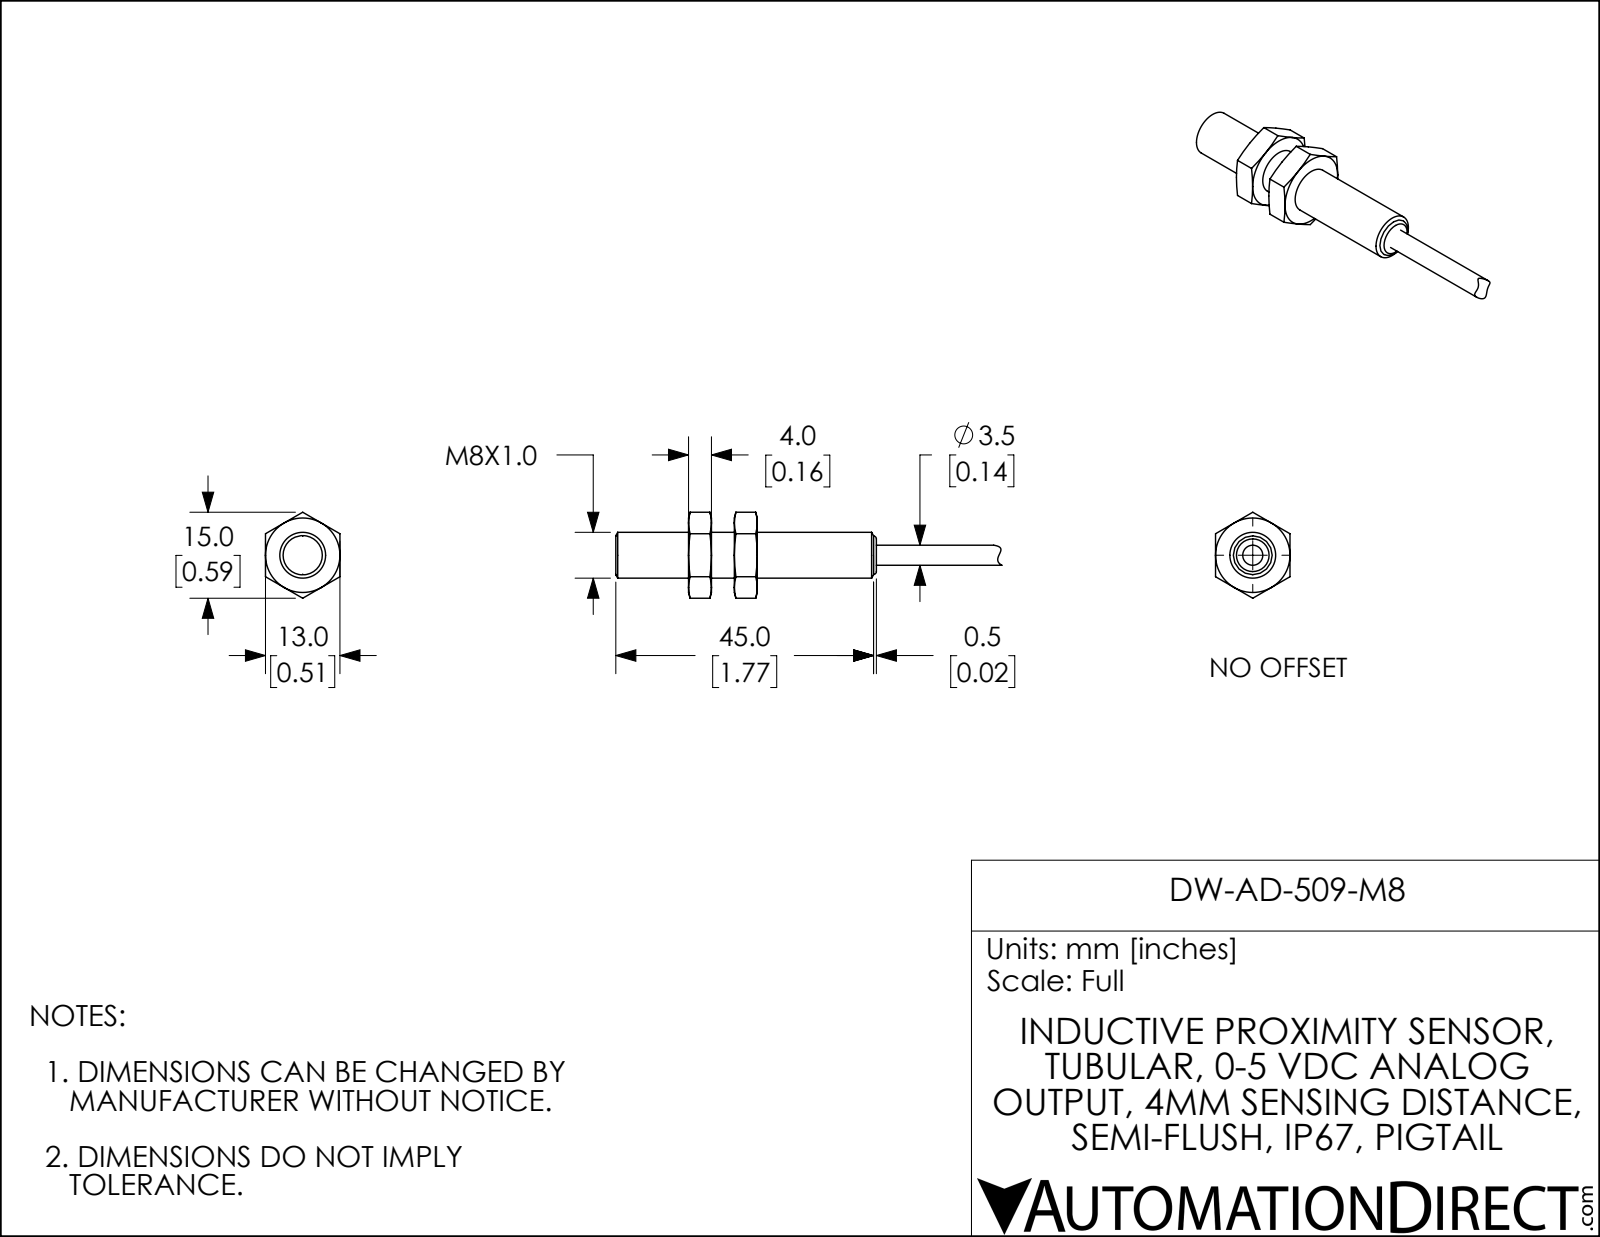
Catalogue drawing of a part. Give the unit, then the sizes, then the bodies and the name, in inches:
Units: inches
Overall size (bounding box): 2.656 × 0.591 × 0.512
Round holes (diameter × count): ⌀0.272 ×1
Round bosses / shafts (diameter × count): ⌀0.315 ×1, ⌀0.138 ×1
Main face-to-face distances: 0.157, 0.512, 0.315, 0.472, 0.5, 0.657, 0.815, 0.972, 1.791, 1.291
Volume: 0.207 in³ · Surface area: 3.836 in²
Bodies: 4 solids, 55 faces (19 planar, 4 cylindrical, 32 other)
Part name (STEP PRODUCT): DW-AD-509-M8
STEP written by: SolidWorks 2018 (AUTOMOTIVE_DESIGN)
